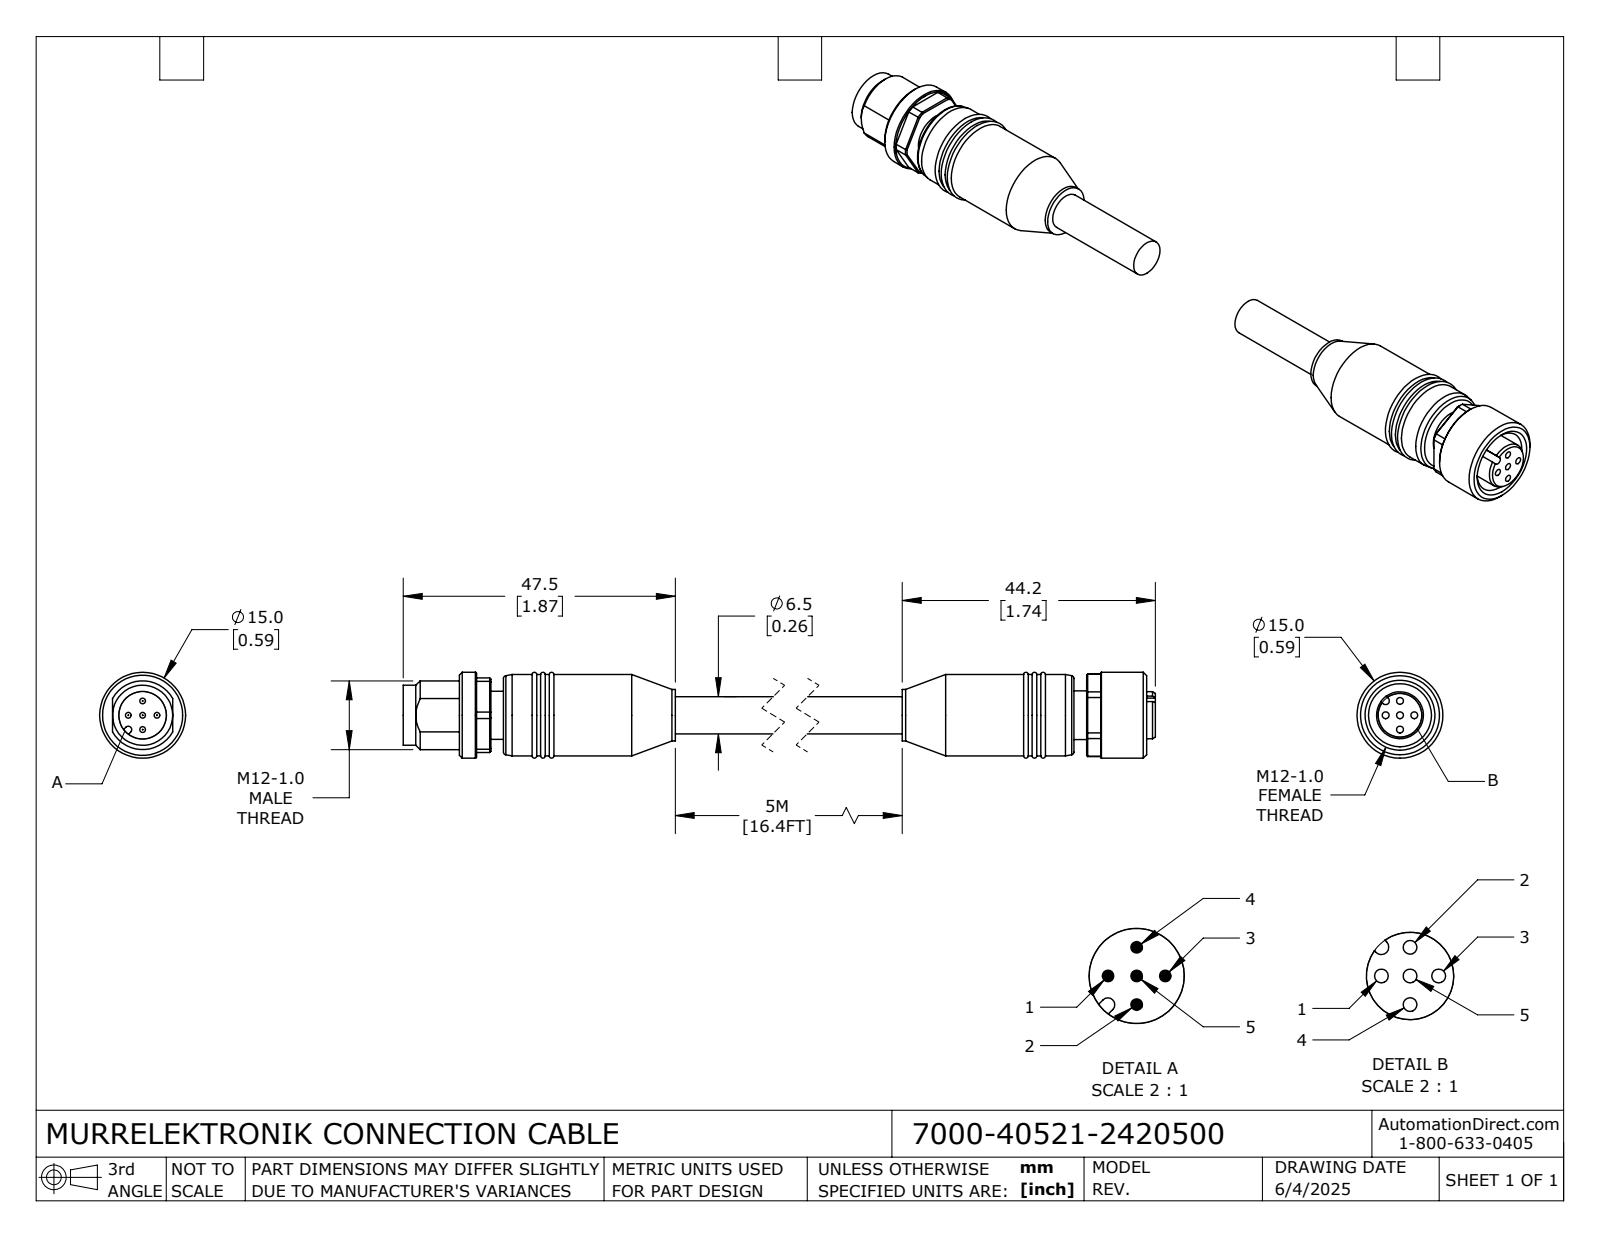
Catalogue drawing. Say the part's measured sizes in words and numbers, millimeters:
The part is named "7000-40521-2420500_MALE; 7000-40521-2420500; 7000-40521-2420500_FEMALE". Its 3-D file was written by "SolidWorks 2024 (CONFIG_CONTROL_DESIGN)". It is 2 solids with 198 faces: 58 planar, 77 cylindrical and 63 other. Overall it measures 156.7 by 15 by 15 millimeters. Its volume is 13 209 cubic millimeters and its surface area 6 539 square millimeters. Round holes: 5 of diameter 1.2, 1 of diameter 8.3, 1 of diameter 11. Round bosses or shafts: 5 of diameter 1, 1 of diameter 15, 1 of diameter 14.2, 1 of diameter 10.5, 1 of diameter 9, 1 of diameter 8.5, 1 of diameter 8.4, 1 of diameter 8.2. Partial cylindrical surfaces (rounded edges, fillets, slot ends): 1 of radius 0.6, 1 of radius 0.65, 1 of radius 6, 1 of radius 7.2. The main face-to-face distances are 2.2, 127.2, 13, 129.4, 10.5, 125, 134.9, 52.2, 77.2, 50. The hole center spacings are 2.5, 3.54, 5.
